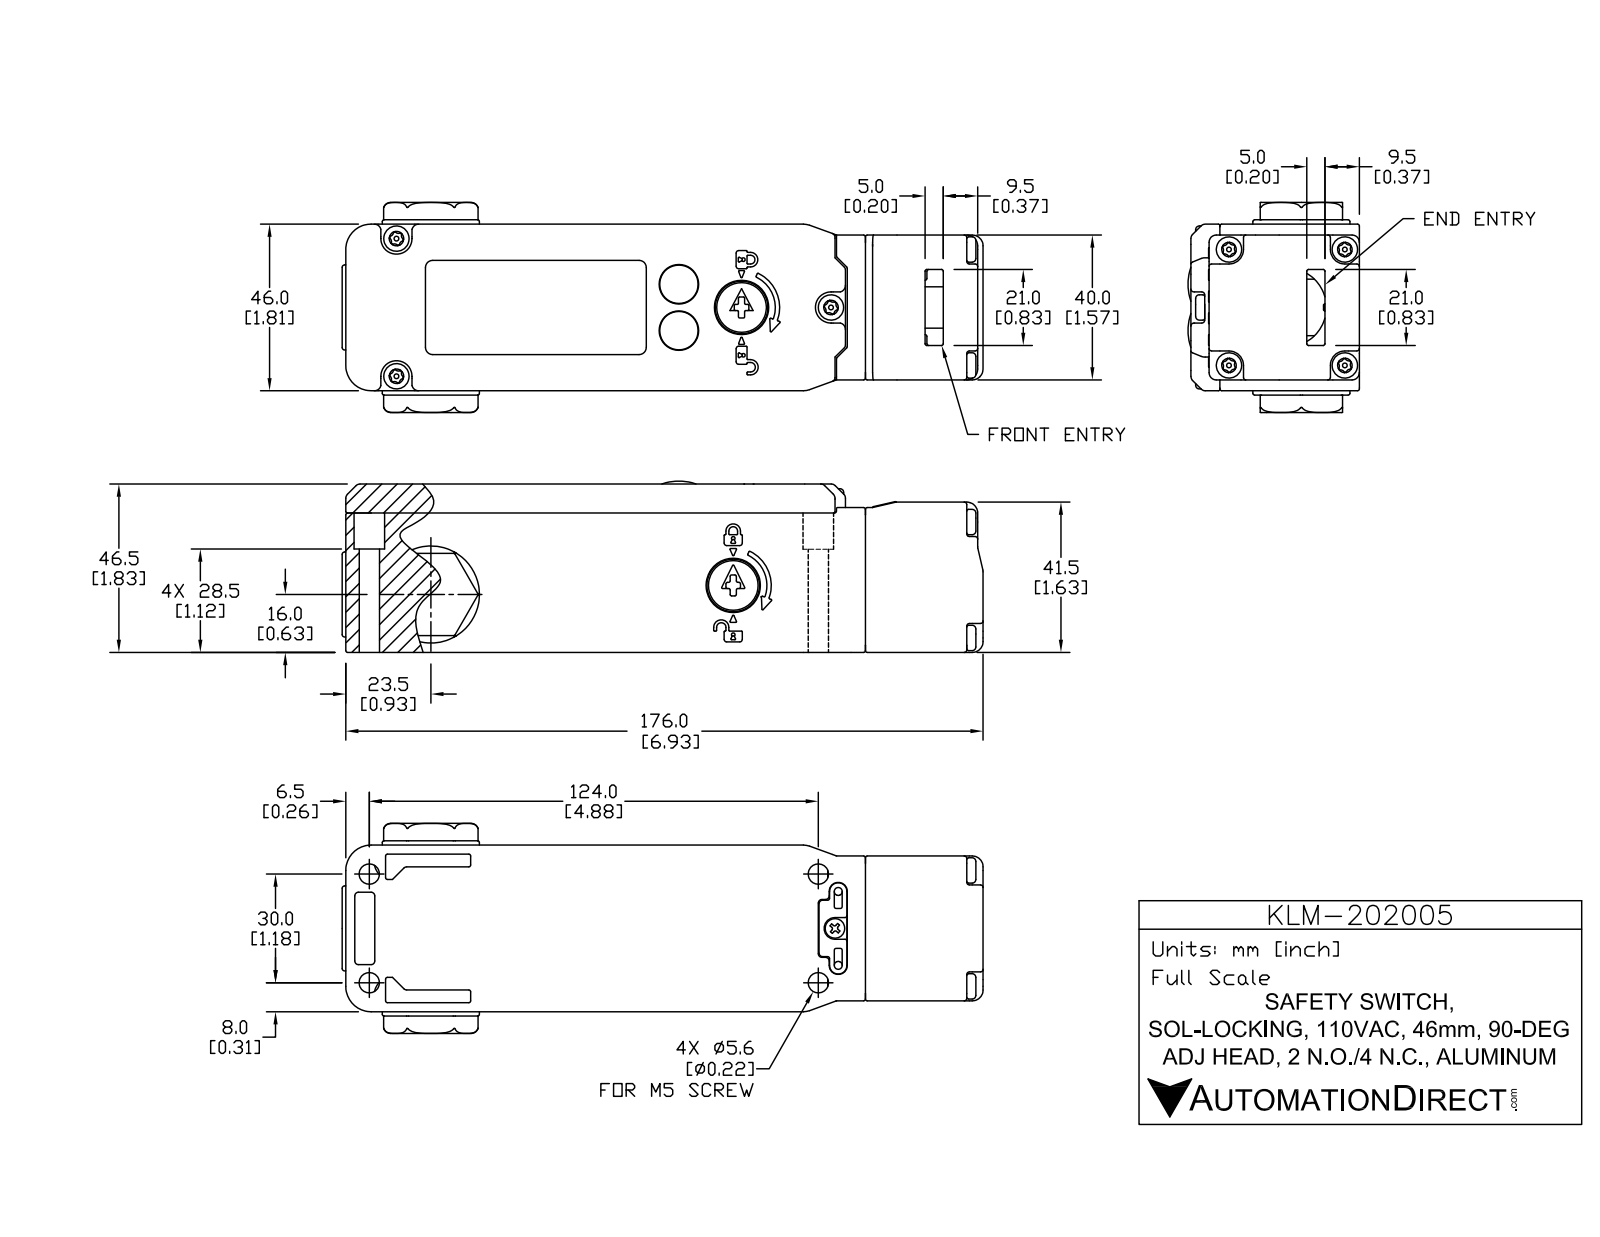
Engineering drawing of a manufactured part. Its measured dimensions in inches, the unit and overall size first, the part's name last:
Units: inches
Overall size (bounding box): 6.969 × 2.283 × 1.861
Round holes (diameter × count): ⌀0.157 ×7, ⌀0.118 ×6, ⌀0.169 ×4, ⌀0.197 ×4, ⌀0.22 ×4, ⌀0.362 ×4, ⌀0.146 ×3, ⌀0.165 ×3, ⌀0.177 ×3, ⌀0.315 ×3, ⌀0.079 ×2, ⌀0.087 ×2
Round bosses / shafts (diameter × count): ⌀0.276 ×7, ⌀0.138 ×7, ⌀0.051 ×7, ⌀0.039 ×4, ⌀0.236 ×3, ⌀0.571 ×2, ⌀0.449 ×2, ⌀0.417 ×2
Partial cylindrical surfaces — rounded edges, fillets, slot ends (radius × count): R0.02 ×519, R0.008 ×139, R0.012 ×115, R0.039 ×111, R0.016 ×70, R0.028 ×42, R0.031 ×36, R0.059 ×25
Main face-to-face distances: 0.091, 1.72, 0.087, 1.811, 0.028, 0.098, 1.602, 0.118, 1.732, 1.646
Hole centre spacings: 0.891, 1.26, 0.139, 0.276, 0.277, 0.287, 0.329, 0.335
Volume: 7.308 in³ · Surface area: 146.4 in²
Bodies: 19 solids, 4517 faces (1071 planar, 1803 cylindrical, 1643 other)
Part name (STEP PRODUCT): KLM-202005
STEP written by: SolidWorks 2017 (AUTOMOTIVE_DESIGN)
